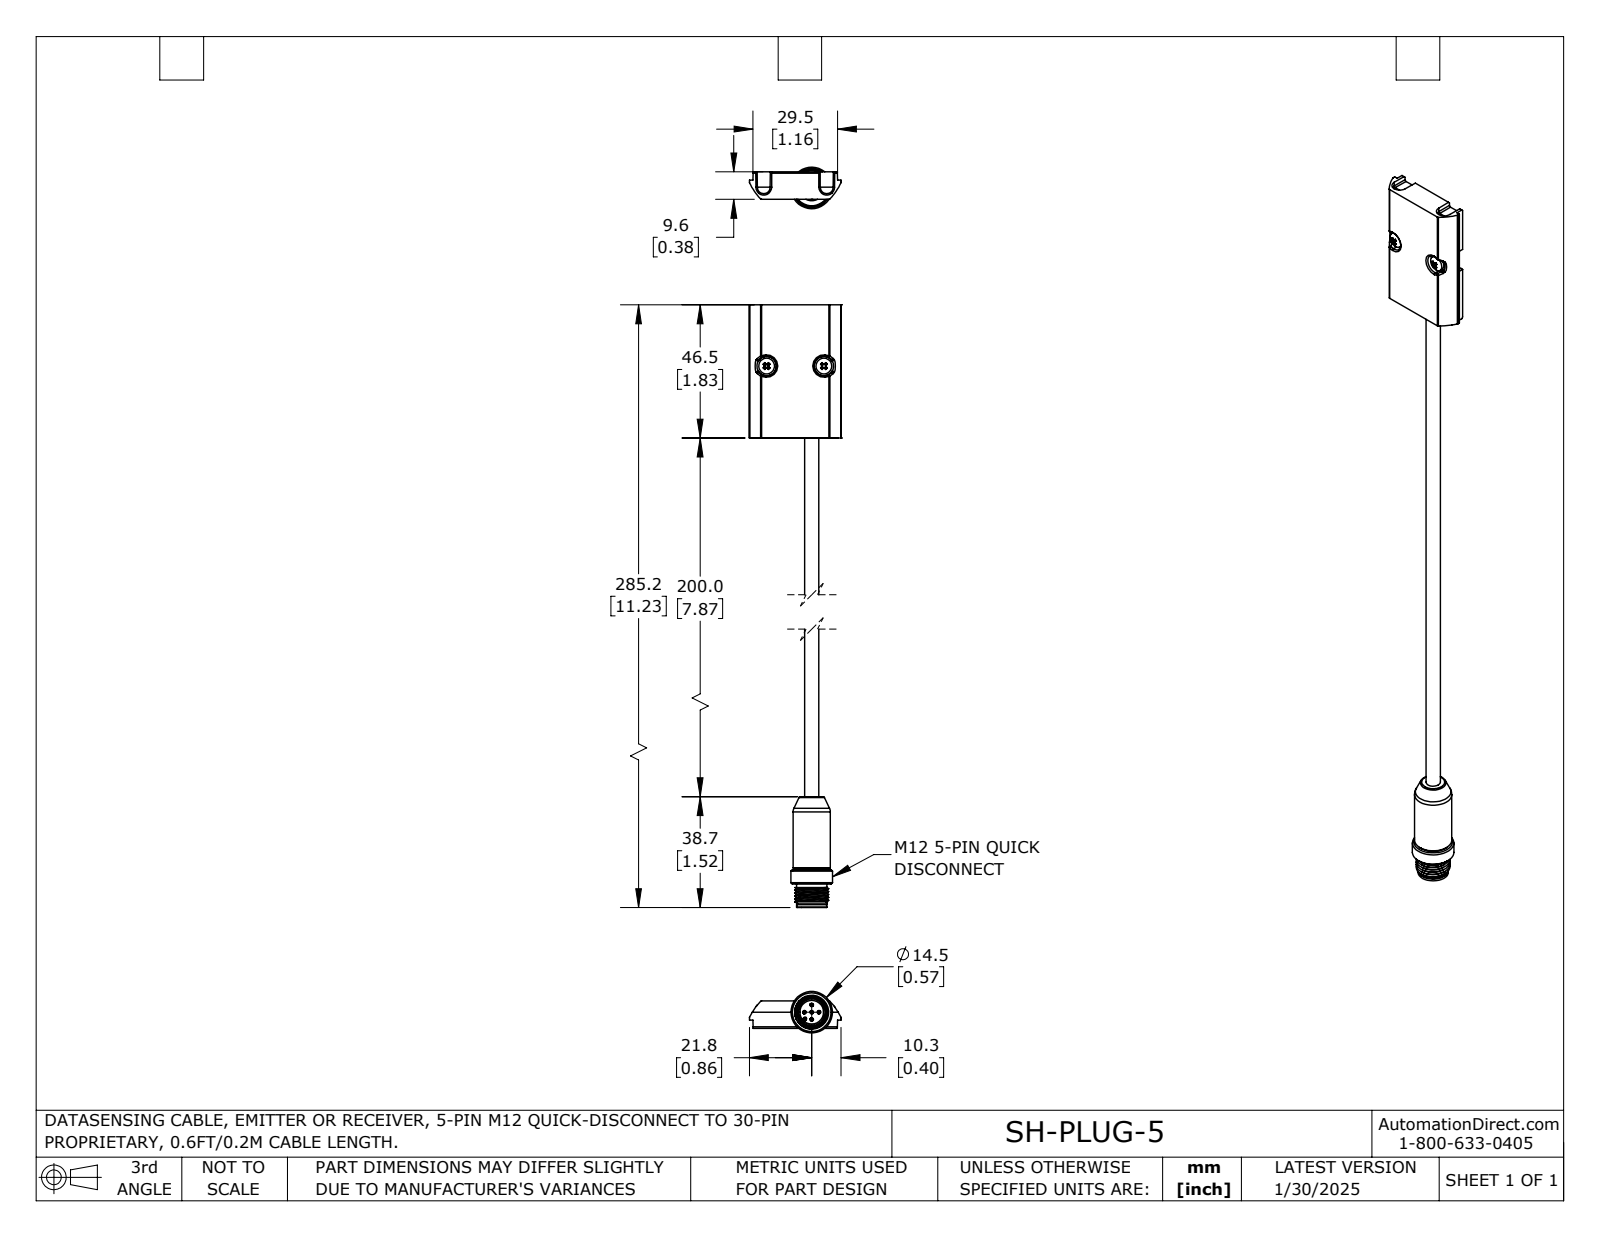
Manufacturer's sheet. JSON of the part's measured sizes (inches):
{"part_name": "SH-PLUG-5", "step_written_by": "SolidWorks 2024 (AUTOMOTIVE_DESIGN)", "units": "inches", "bodies": {"solids": 1, "faces": 401, "planar": 216, "cylindrical": 77, "other": 108}, "overall_size": [11.228, 1.26, 0.571], "volume_in3": 0.729, "surface_area_in2": 23.76, "round_holes": [[0.11, 1], [0.325, 1], [0.382, 1], [0.407, 1], [0.425, 1]], "round_bosses_or_shafts": [[0.039, 5], [0.217, 2], [0.571, 1], [0.512, 1], [0.417, 1], [0.374, 1], [0.197, 1]], "partial_cylinders_radius": [[0.02, 13], [0.008, 10], [0.012, 2], [0.108, 2], [0.138, 2], [0.197, 2], [0.728, 2], [0.748, 2]], "face_to_face_distances": [0.147, 0.059, 0.088, 0.056, 0.032, 0.091, 0.378, 0.322, 0.29, 0.231]}
